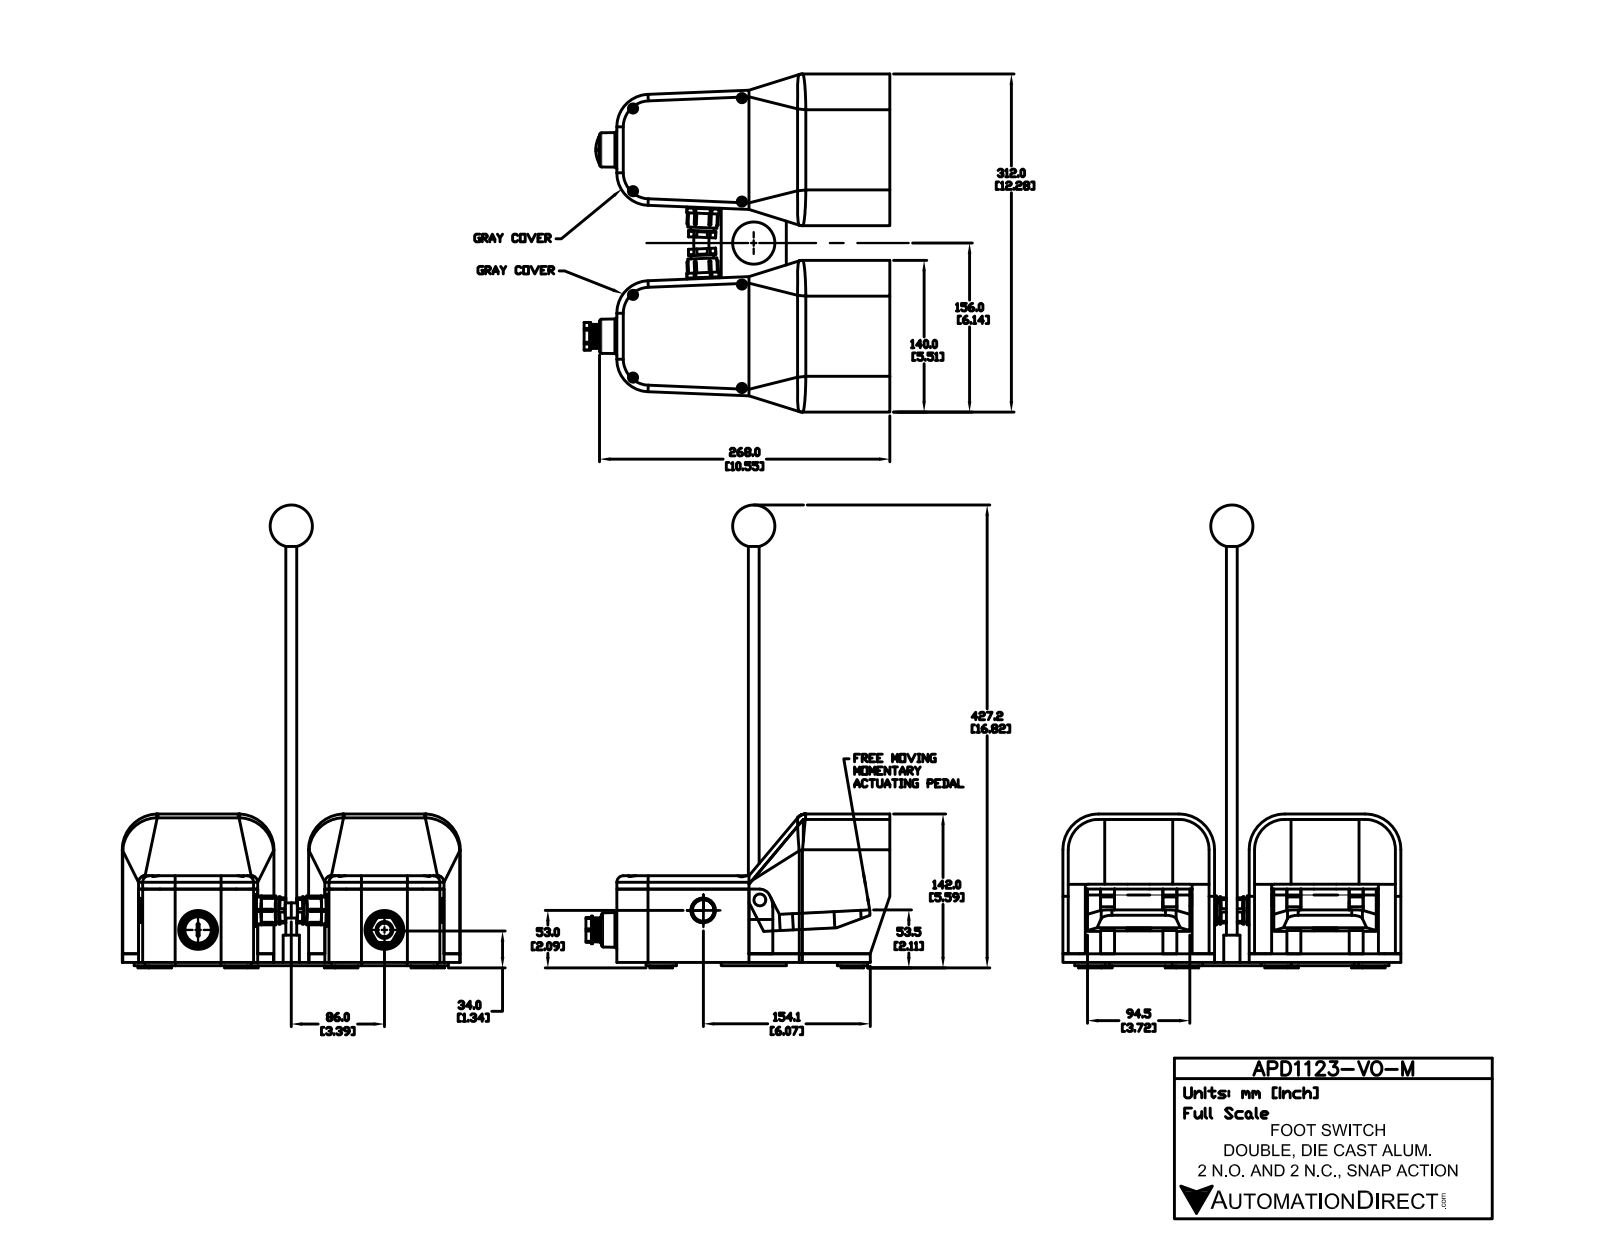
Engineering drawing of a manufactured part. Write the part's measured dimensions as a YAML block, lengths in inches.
part_name: "APD1123-V0-M"
step_written_by: "SolidWorks 2015 (AUTOMOTIVE_DESIGN)"
units: inches
bodies: {solids: 36, faces: 829, planar: 502, cylindrical: 213, other: 114}
overall_size: [16.817, 12.283, 11.112]
volume: 196.2
surface_area: 892.6
round_holes:
  - {diameter: 0.335, count: 8}
  - {diameter: 0.896, count: 4}
  - {diameter: 0.498, count: 1}
  - {diameter: 0.614, count: 1}
round_bosses_or_shafts:
  - {diameter: 1.102, count: 8}
  - {diameter: 0.827, count: 8}
  - {diameter: 0.782, count: 4}
  - {diameter: 1.171, count: 2}
  - {diameter: 1.051, count: 2}
  - {diameter: 0.992, count: 2}
  - {diameter: 0.846, count: 2}
  - {diameter: 1.004, count: 1}
partial_cylinders:
  - {radius: 0.039, count: 34}
  - {radius: 0.042, count: 12}
  - {radius: 0.394, count: 10}
  - {radius: 0.236, count: 5}
  - {radius: 1.102, count: 4}
  - {radius: 1.181, count: 4}
  - {radius: 1.299, count: 4}
  - {radius: 0.787, count: 1}
face_to_face_distances: [0.197, 5.315, 6.772, 0.315, 2.348, 5.512, 2.664, 2.349, 2.663, 0.118]
hole_center_spacings: [3.976, 5.206, 6.772, 3.004, 3.76, 5.211, 7.52, 8.172]
